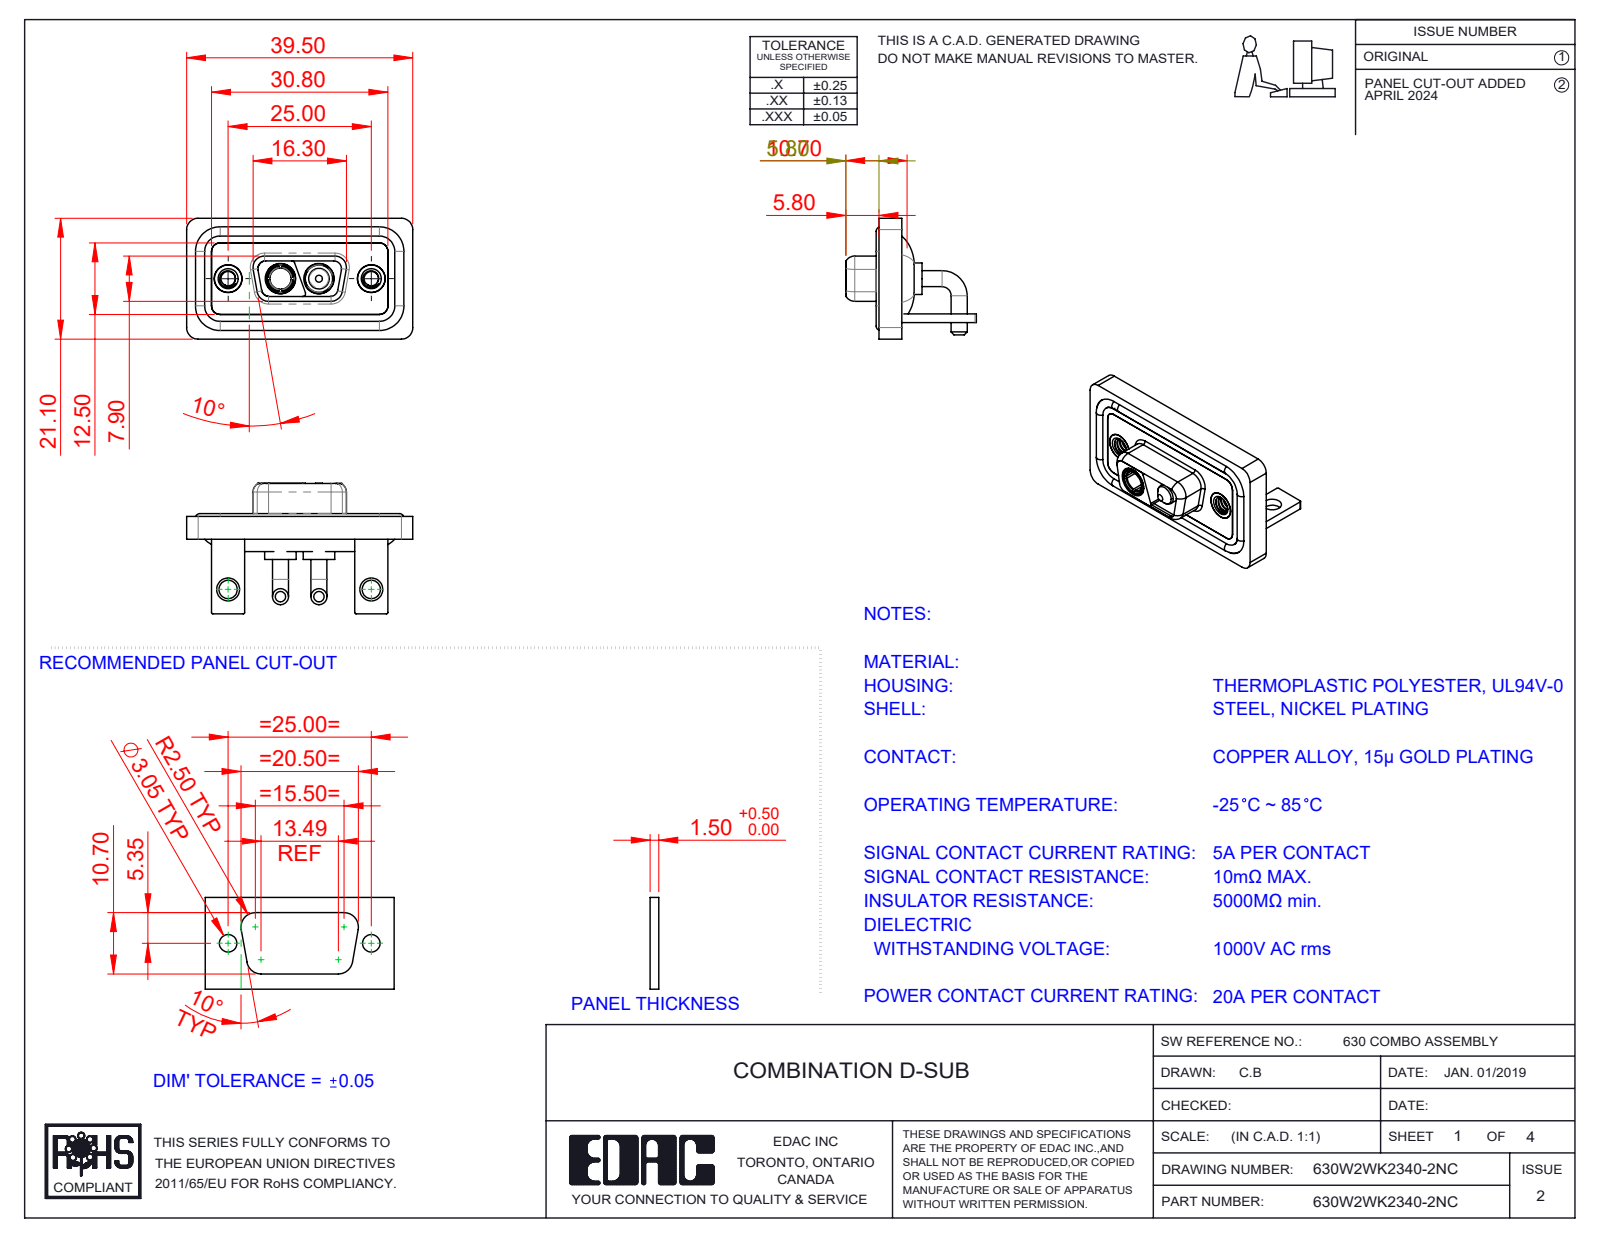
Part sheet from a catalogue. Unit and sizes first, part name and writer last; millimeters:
Units: millimetres
Overall size (bounding box): 39.5 × 22.8 × 21.1
Round holes (diameter × count): ⌀4.85 ×4, ⌀2.5 ×2, ⌀3.2 ×2, ⌀4 ×2, ⌀4.05 ×2, ⌀5 ×2, ⌀5.3 ×2, ⌀3.7 ×1
Round bosses / shafts (diameter × count): ⌀2.8 ×4, ⌀1.6 ×4, ⌀5.5 ×2, ⌀5.2 ×2, ⌀4.95 ×2, ⌀4.8 ×2, ⌀4.75 ×2, ⌀3.75 ×2
Partial cylindrical surfaces — rounded edges, fillets, slot ends (radius × count): R2 ×19, R1.5 ×18, R0.25 ×16, R1.35 ×8, R1.6 ×8, R0.5 ×7, R0.6 ×4, R0.65 ×4
Main face-to-face distances: 0.4, 2.9, 1.5, 1.1, 3.7, 1.8, 0.8, 2.5, 1.6, 3.1
Hole centre spacings: 9.14, 15.86, 25, 6.72
Volume: 5 066 mm³ · Surface area: 8 233 mm²
Bodies: 13 solids, 550 faces (164 planar, 257 cylindrical, 129 other)
Part name (STEP PRODUCT): 630Combo Shell Rear_09 Contacts; 630Combo Threaded Rivet_A; Power Pin_20A RA; 630Combo Housing_2WK2 (+5 more)
STEP written by: SolidWorks 2023 (CONFIG_CONTROL_DESIGN)
